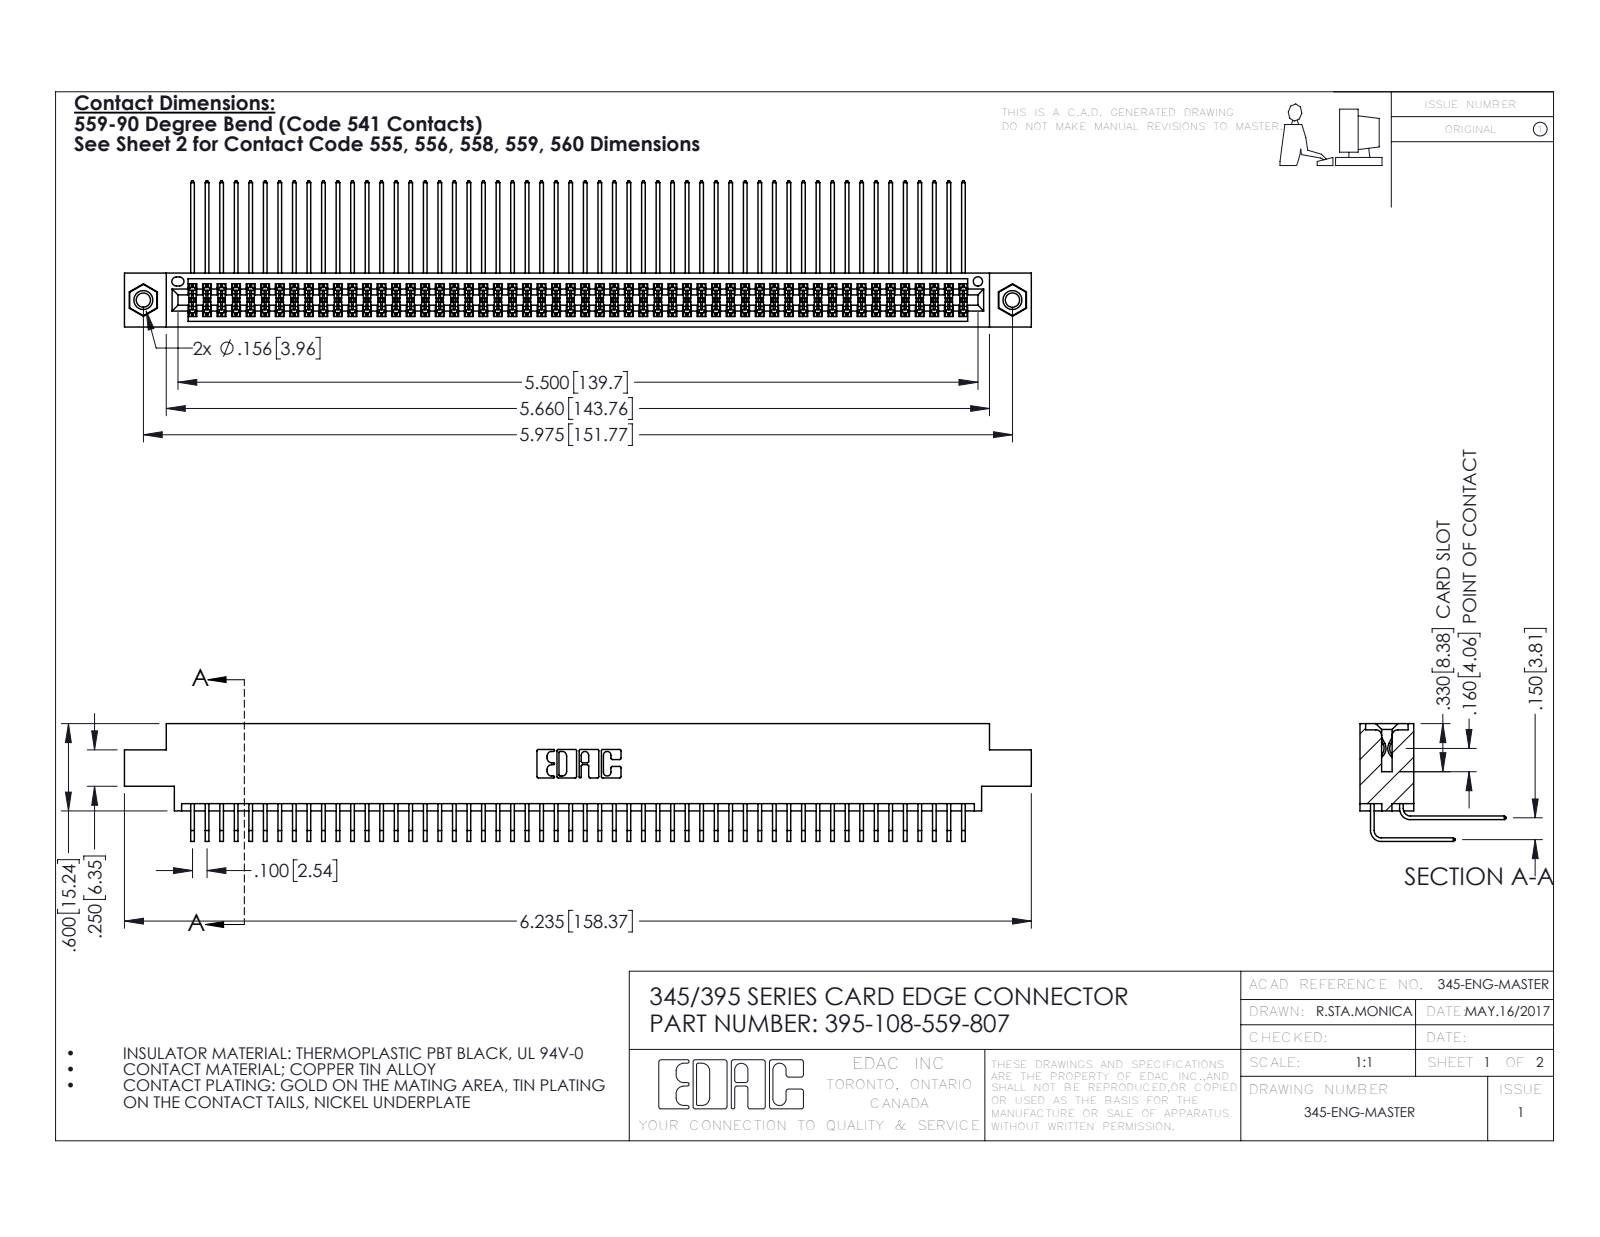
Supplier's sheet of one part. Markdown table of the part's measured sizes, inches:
| quantity | value |
| --- | --- |
| part name | 345-250-001_345-250-005-103; 345 Part_0.170 Offset - 0.156 Dia-TI; 395-108-559-807; 345-292-001_558 559 Tail - 1 (+1 more) |
| STEP written by | SolidWorks 2016 (CONFIG_CONTROL_DESIGN) |
| units | inches |
| bodies | 111 solids, 5806 faces (3896 planar, 1894 cylindrical, 16 other) |
| overall size | 6.235 × 1.005 × 0.809 |
| volume | 0.976 in³ |
| surface area | 41.81 in² |
| round holes (diameter × count) | 0.098 × 2, 0.125 × 2, 0.156 × 2, 0.064 × 1 |
| round bosses / shafts (diameter × count) | 0.155 × 2 |
| partial cylindrical surfaces (radius × count) | 0.006 × 162, 0.01 × 22, 0.007 × 6, 0.031 × 6, 0.026 × 3, 0.014 × 2, 0.019 × 2, 0.022 × 2 |
| main face-to-face distances | 0.072, 0.298, 0.37, 0.2, 0.098, 0.272, 0.025, 0.225, 0.175, 0.15 |
| hole center spacings | 0.27, 5.739, 5.975 |
